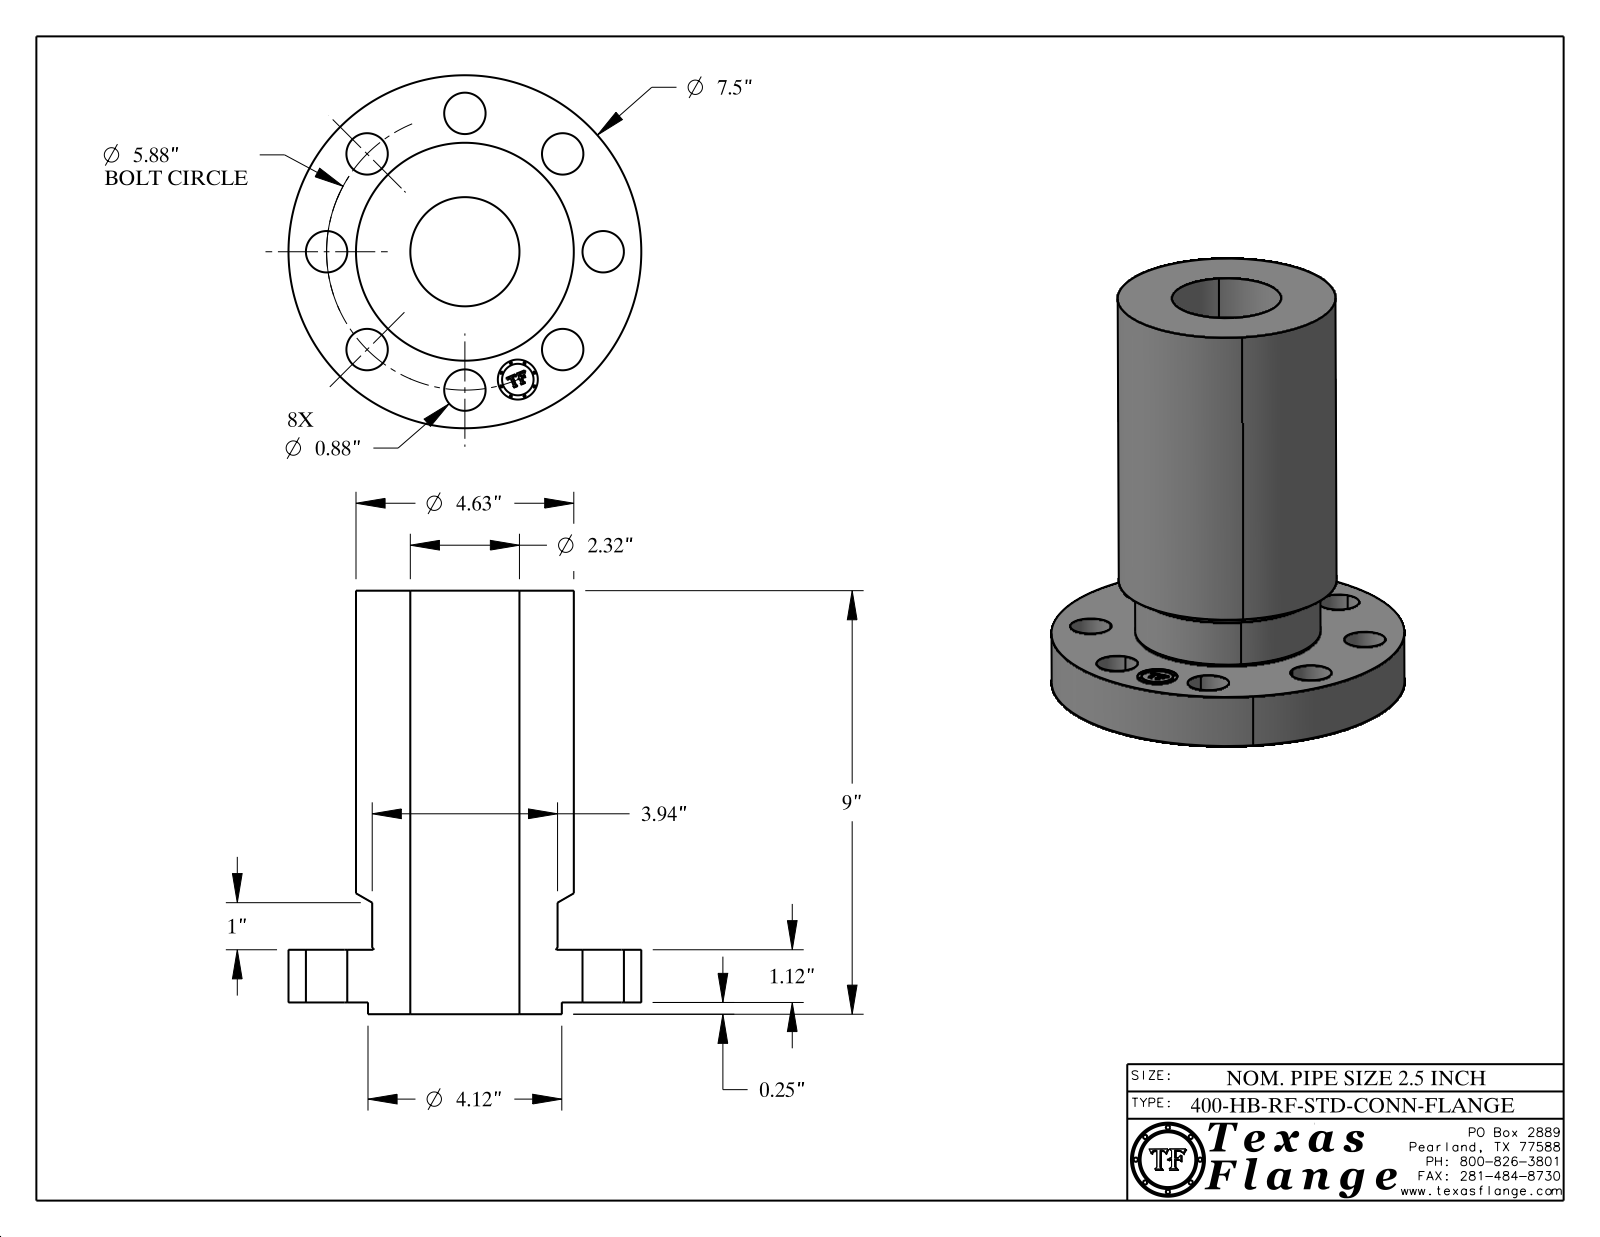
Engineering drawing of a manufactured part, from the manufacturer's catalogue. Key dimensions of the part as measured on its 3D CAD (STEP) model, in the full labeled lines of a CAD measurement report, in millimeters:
Part name (STEP PRODUCT): 2.5-400-HB-RF-STD-CONN-FLANGE
STEP written by: CATIA V5 STEP AP214 (AUTOMOTIVE_DESIGN)
Units: millimetres
Bodies: 1 solid, 421 faces (369 planar, 46 cylindrical, 6 other)
Overall size (bounding box): 228.6 × 190.5 × 190.5
Volume: 2 173 000 mm³ · Surface area: 197 800 mm²
Round holes (diameter × count): ⌀22.4 ×8, ⌀21.6 ×1, ⌀58.9 ×1
Round bosses / shafts (diameter × count): ⌀1.3 ×8, ⌀190.5 ×1, ⌀117.6 ×1, ⌀104.6 ×1, ⌀100.1 ×1, ⌀17 ×1
Main face-to-face distances: 28.4, 222.3, 193.8, 6.4, 34.8, 228.6, 34.7, 28.3, 193.9, 6.5
Hole centre spacings: 57.2, 138, 74.7, 74.7, 105.6, 105.6, 83, 149.4
